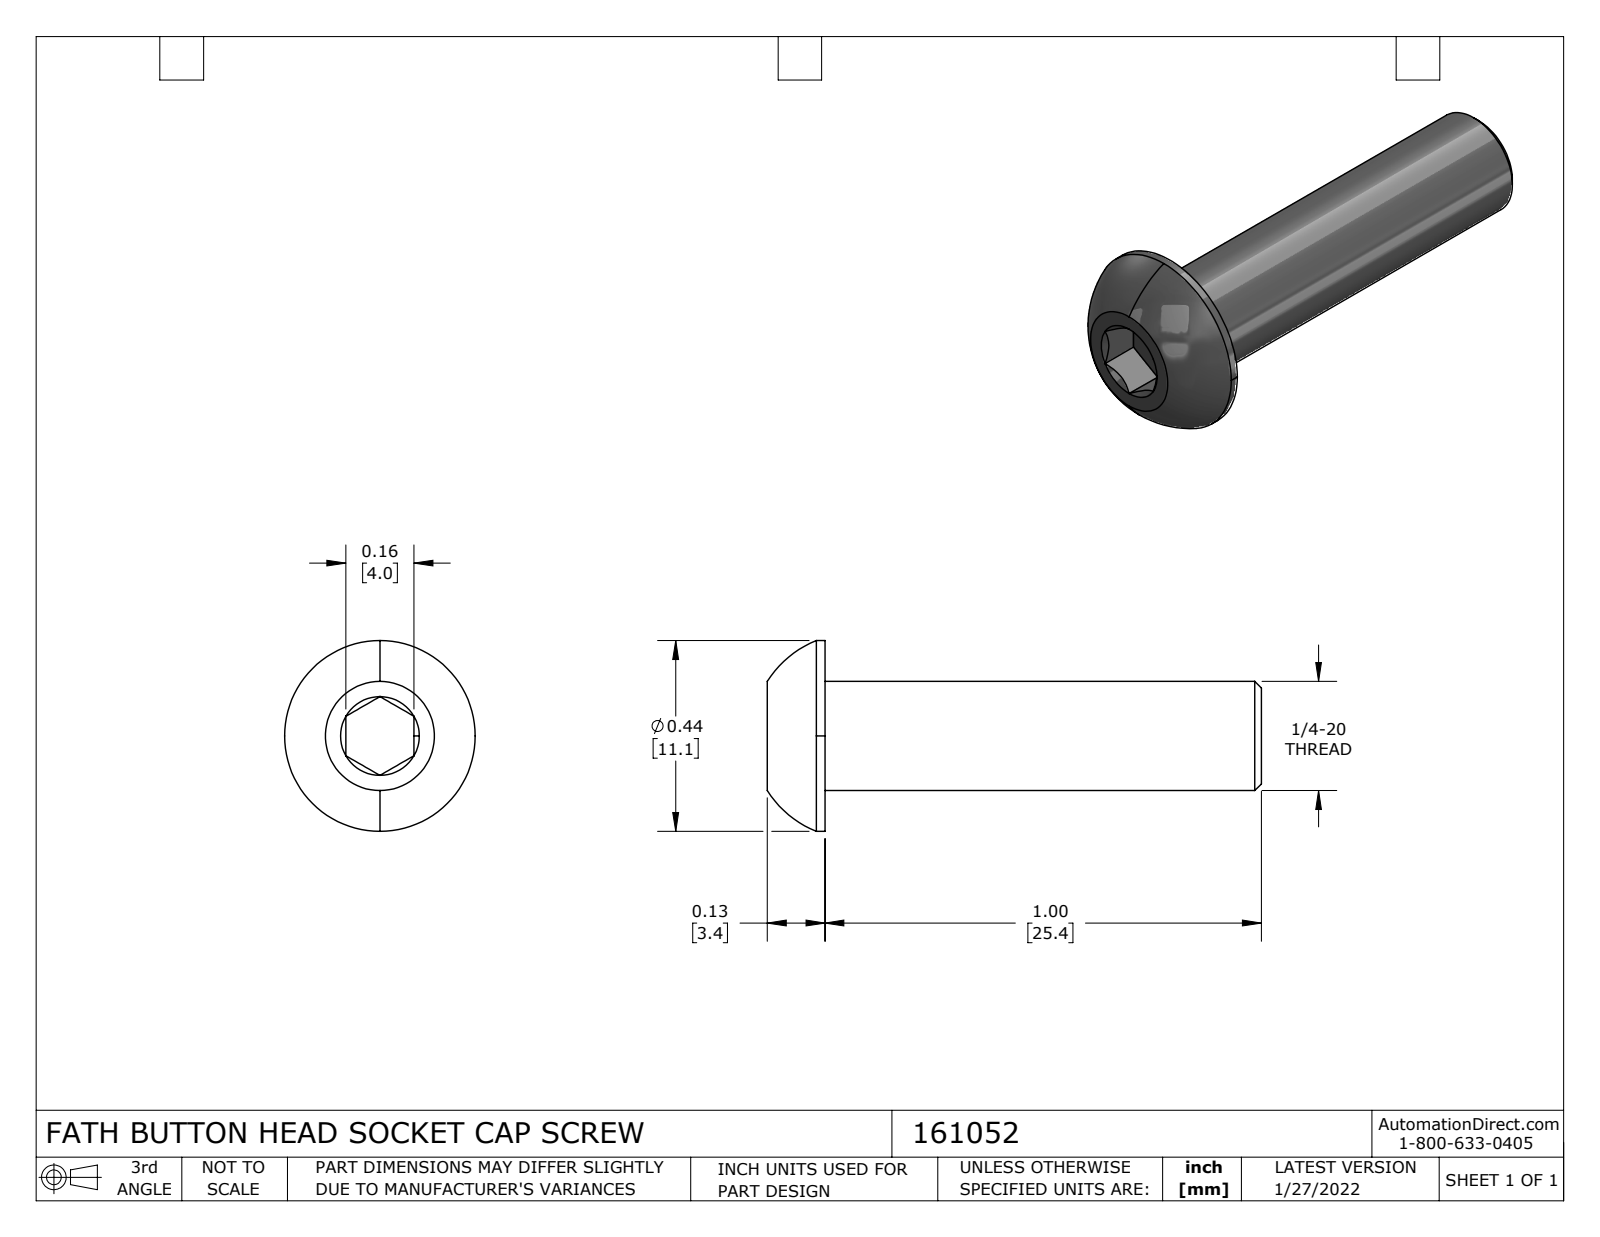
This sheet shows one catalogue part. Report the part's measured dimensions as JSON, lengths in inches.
{"part_name": "161052", "step_written_by": "SolidWorks 2021 (CONFIG_CONTROL_DESIGN)", "units": "inches", "bodies": {"solids": 1, "faces": 29, "planar": 12, "cylindrical": 4, "other": 13}, "overall_size": [1.132, 0.437, 0.437], "volume_in3": 0.062, "surface_area_in2": 1.223, "round_bosses_or_shafts": [[0.437, 1], [0.25, 1]], "face_to_face_distances": [1, 1.132, 0.132, 1.039, 0.039, 0.093, 0.156, 0.078]}
